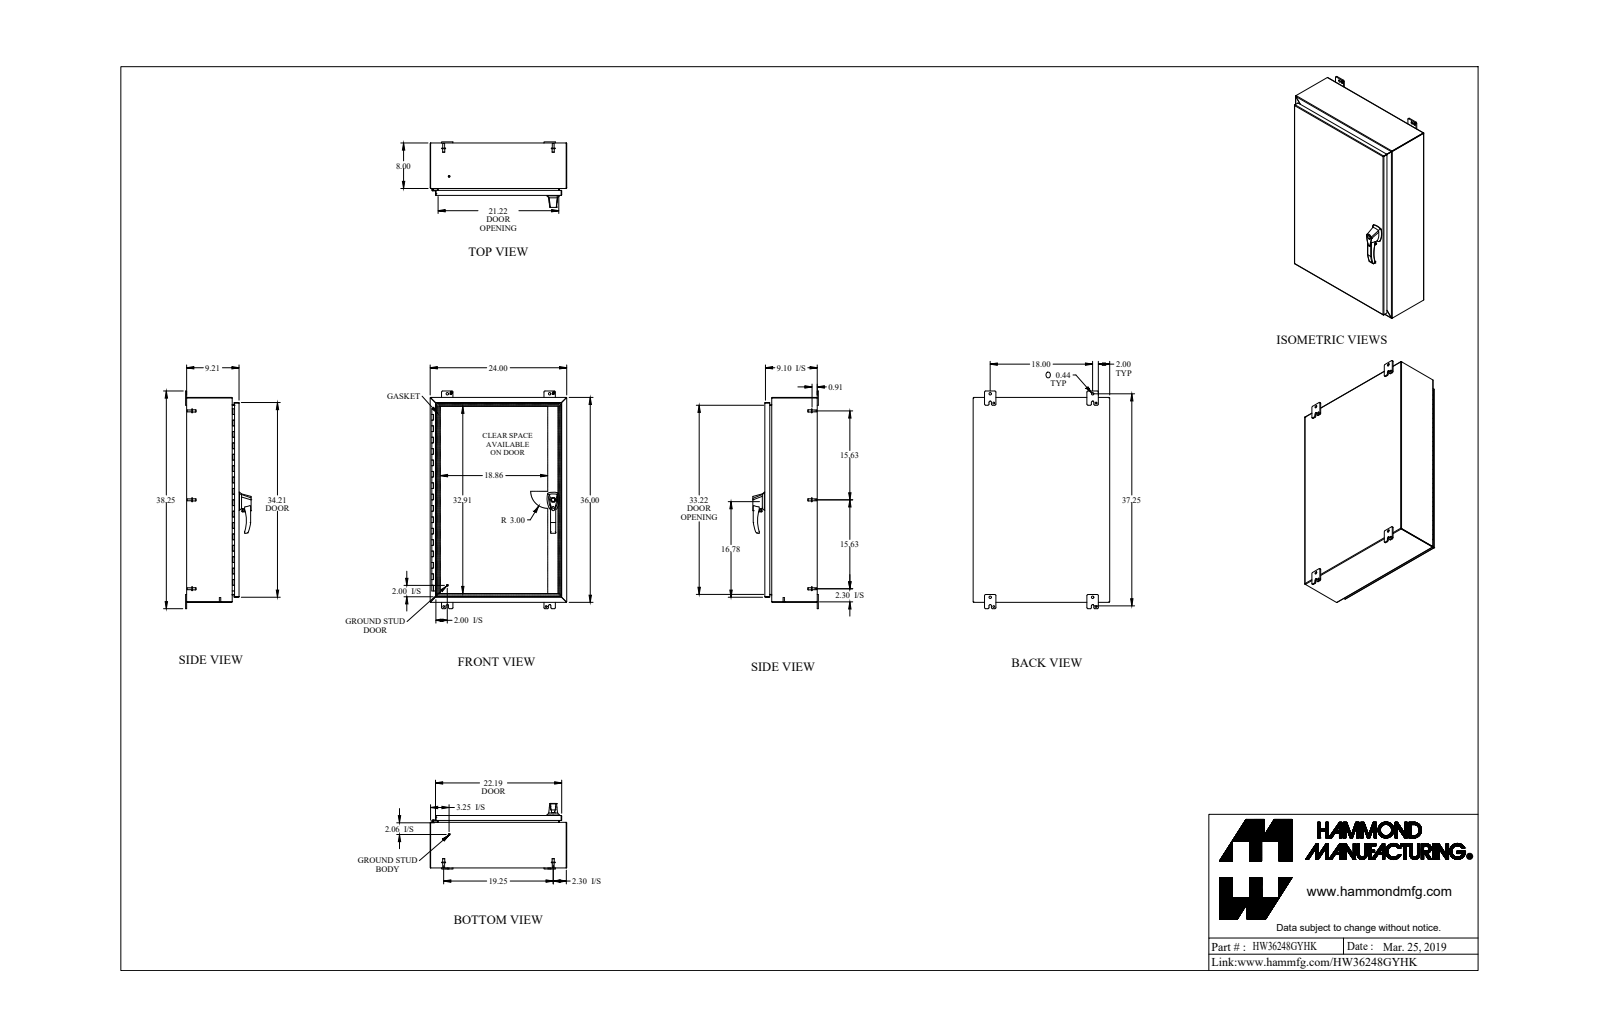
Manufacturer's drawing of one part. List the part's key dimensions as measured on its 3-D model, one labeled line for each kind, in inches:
Part name (STEP PRODUCT): HW36248GYHK
STEP written by: SolidWorks 2018 (AUTOMOTIVE_DESIGN)
Units: inches
Bodies: 43 solids, 1549 faces (747 planar, 629 cylindrical, 173 other)
Overall size (bounding box): 38.25 × 24 × 11.512
Volume: 254.3 in³ · Surface area: 6 600 in²
Round holes (diameter × count): ⌀0.176 ×6, ⌀0.25 ×4, ⌀0.313 ×4, ⌀0.196 ×3, ⌀0.265 ×3, ⌀0.413 ×3, ⌀0.256 ×2, ⌀0.394 ×2, ⌀0.437 ×2, ⌀0.187 ×1, ⌀0.233 ×1, ⌀0.334 ×1
Round bosses / shafts (diameter × count): ⌀0.375 ×11, ⌀0.65 ×6, ⌀0.33 ×6, ⌀0.25 ×6, ⌀0.156 ×6, ⌀1 ×3, ⌀0.63 ×2, ⌀0.51 ×2
Partial cylindrical surfaces — rounded edges, fillets, slot ends (radius × count): R0.25 ×27, R0.188 ×24, R0.036 ×20, R0.108 ×20, R0.06 ×12, R0.125 ×9, R0.045 ×8, R0.218 ×8
Main face-to-face distances: 0.072, 9.138, 9.066, 0.072, 9.21, 9.138, 23.928, 35.928, 7.928, 23.856
Hole centre spacings: 14.118, 14.119, 28.237, 1.111, 9.698, 14.119, 18, 26.316
